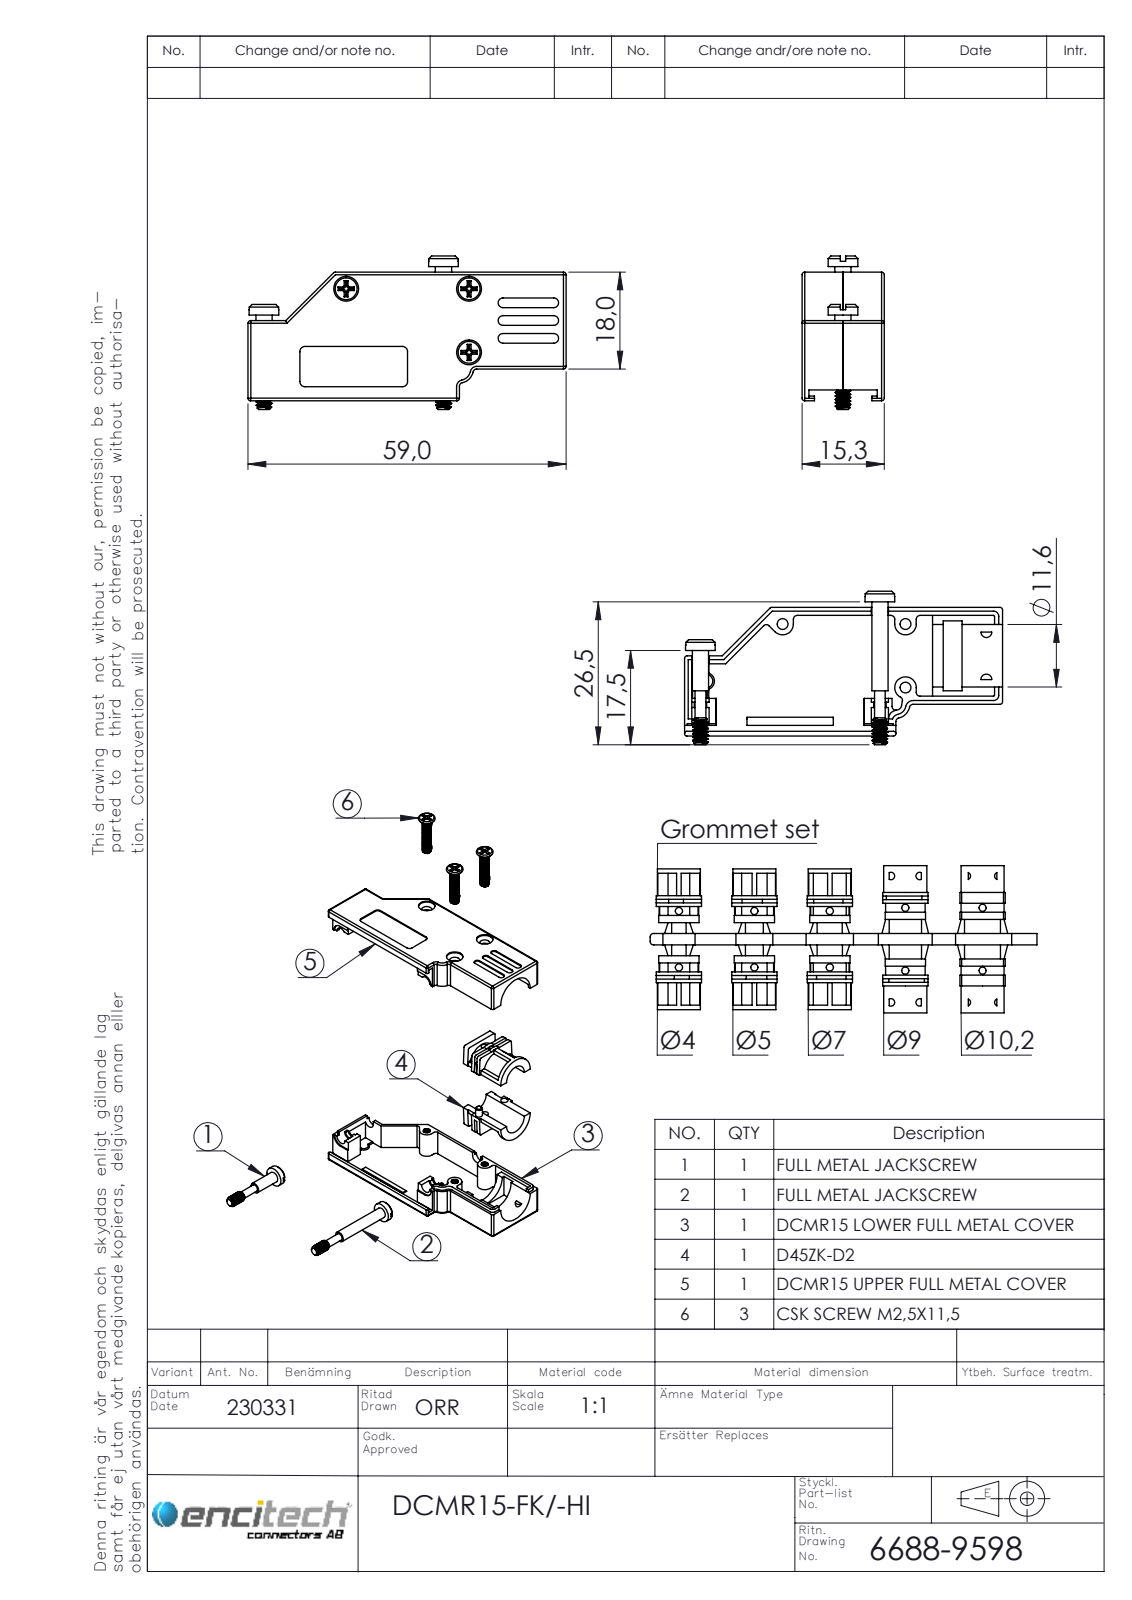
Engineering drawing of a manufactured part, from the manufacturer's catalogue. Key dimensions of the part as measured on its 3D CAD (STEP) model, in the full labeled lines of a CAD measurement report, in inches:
Part name (STEP PRODUCT): 6688-9598; 6855-0115-03; 6826-0128-11; 6826-0128-13 (+3 more)
STEP written by: SolidWorks 2021 (AUTOMOTIVE_DESIGN)
Units: inches
Bodies: 9 solids, 891 faces (336 planar, 454 cylindrical, 101 other)
Overall size (bounding box): 2.323 × 1.122 × 0.606
Volume: 0.472 in³ · Surface area: 17.95 in²
Round holes (diameter × count): ⌀0.079 ×6, ⌀0.11 ×3, ⌀0.181 ×3, ⌀0.126 ×2, ⌀0.276 ×1, ⌀0.457 ×1
Round bosses / shafts (diameter × count): ⌀0.098 ×3, ⌀0.217 ×2, ⌀0.118 ×2, ⌀0.112 ×2, ⌀0.079 ×2, ⌀0.075 ×2, ⌀0.362 ×1
Partial cylindrical surfaces — rounded edges, fillets, slot ends (radius × count): R0.02 ×28, R0.028 ×9, R0.039 ×8, R0.035 ×6, R0.012 ×4, R0.233 ×4, R0.079 ×3, R0.008 ×2
Main face-to-face distances: 0.051, 0.549, 0.039, 0.6, 0.498, 0.059, 0.25, 0.537, 0.079, 0.287
Hole centre spacings: 0.225, 0.328, 0.343, 0.548, 0.394, 0.465, 0.898, 1.011
